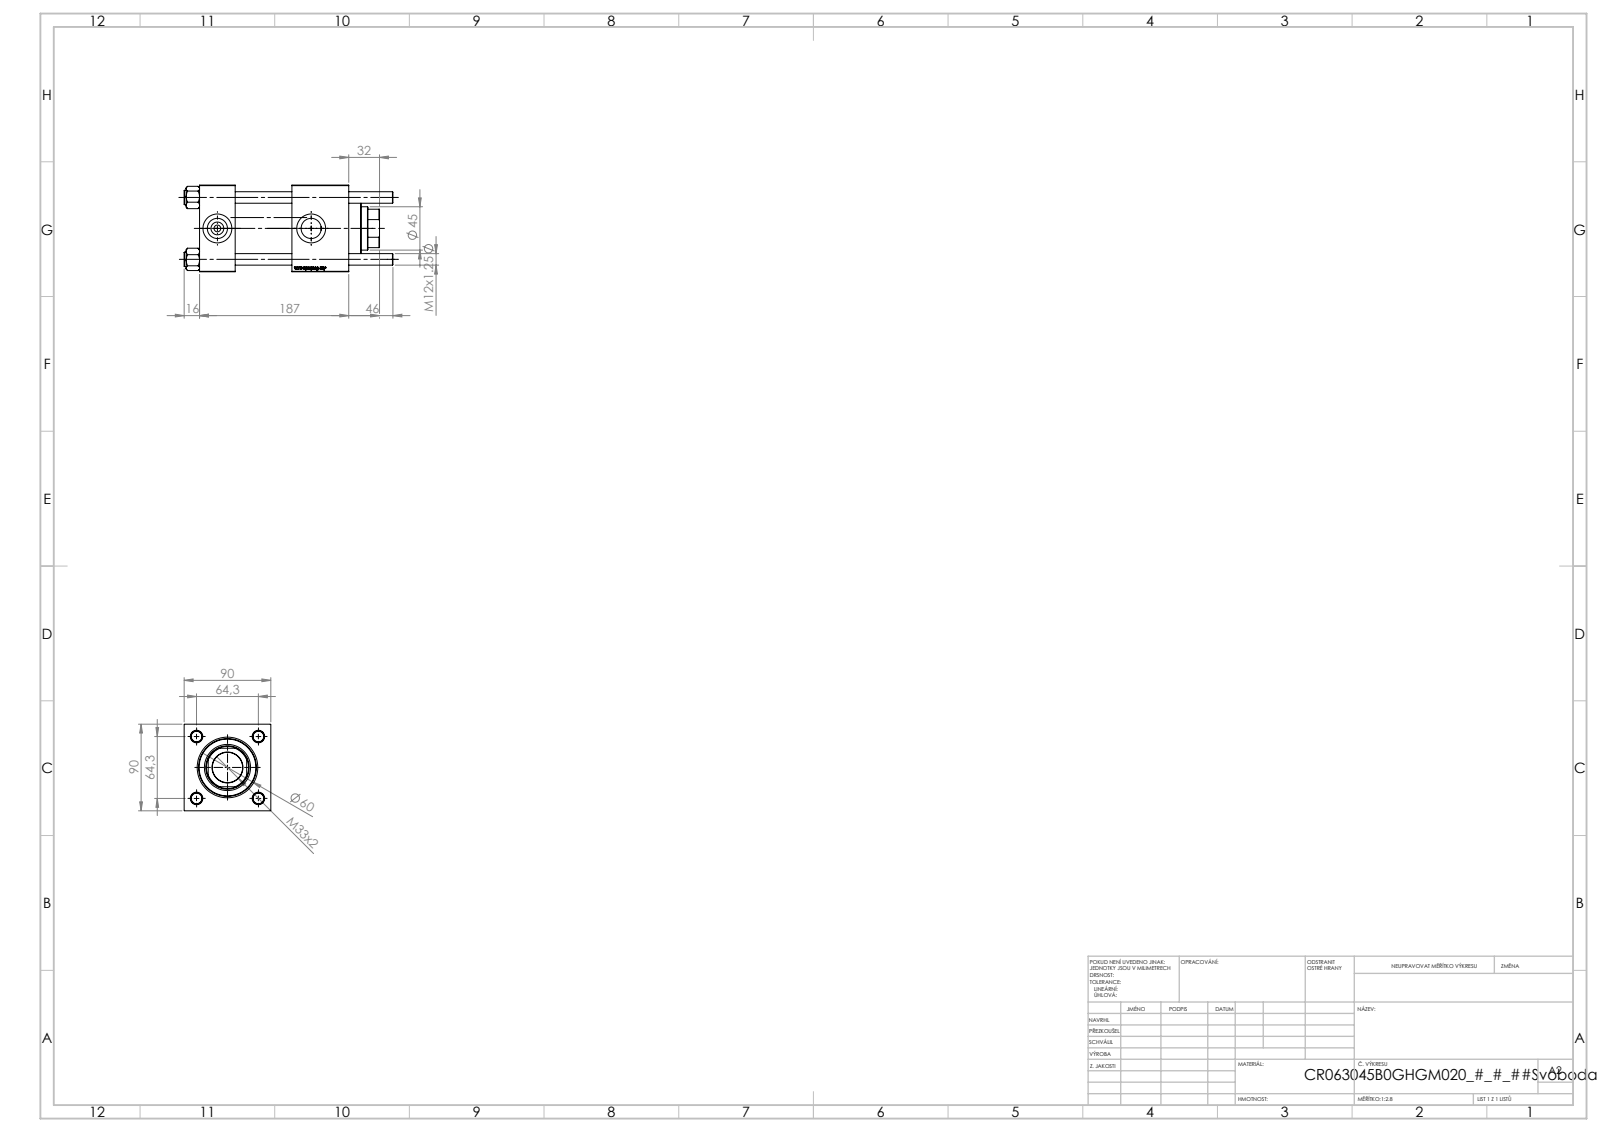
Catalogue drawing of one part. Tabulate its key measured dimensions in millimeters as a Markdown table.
| quantity | value |
| --- | --- |
| part name | V215_VC_A; V215CR_B_TYCINKA; V215CR_B-1; NUT_M5_B (+1 more) |
| STEP written by | SolidWorks 2019 (CONFIG_CONTROL_DESIGN) |
| units | millimeters |
| bodies | 11 solids, 1155 faces (431 planar, 76 cylindrical, 648 other) |
| overall size | 217 × 90 × 90 |
| volume | 1 032 000 mm³ |
| surface area | 205 813 mm² |
| round holes (diameter × count) | 12 × 4, 7 × 2, 20.96 × 2, 30 × 2, 31.5 × 1, 45 × 1, 48 × 1, 50 × 1, 60 × 1, 63 × 1 |
| round bosses / shafts (diameter × count) | 15 × 4, 69 × 1 |
| partial cylindrical surfaces (radius × count) | 22 × 1 |
| main face-to-face distances | 90, 59, 37, 96, 155, 118, 126.3, 89.3, 30.3, 28.7 |
| hole center spacings | 45.47, 64.3, 90.93, 97.5 |
